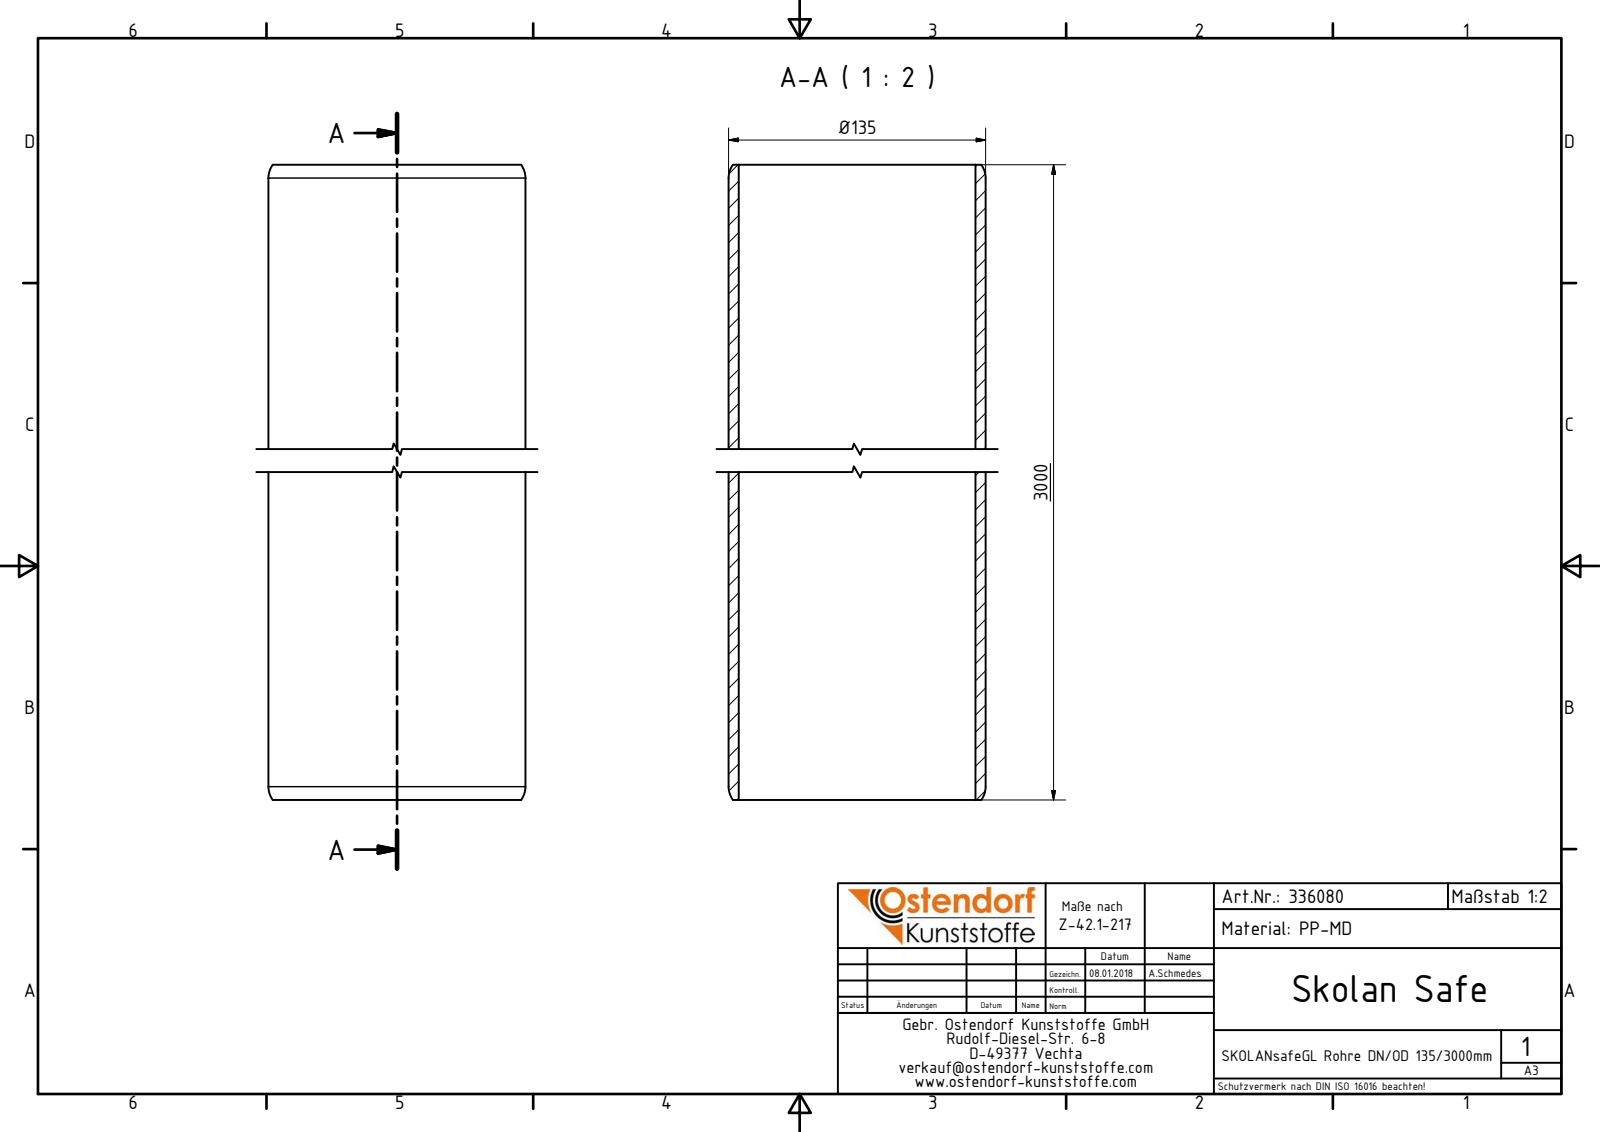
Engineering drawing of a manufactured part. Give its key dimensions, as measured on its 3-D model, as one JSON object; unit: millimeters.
{"part_name": "336080 SKOLANsafeGL Rohr ohne Muffe DN_OD 135x3000mm", "step_written_by": "Autodesk Inventor 2016 (AUTOMOTIVE_DESIGN)", "units": "millimeters", "bodies": {"solids": 1, "faces": 6, "planar": 2, "cylindrical": 2, "other": 2}, "overall_size": [3000, 135, 135], "volume_mm3": 6474000, "surface_area_mm2": 2448000, "round_holes": [[124.4, 1]], "round_bosses_or_shafts": [[135, 1]], "face_to_face_distances": [3000]}
